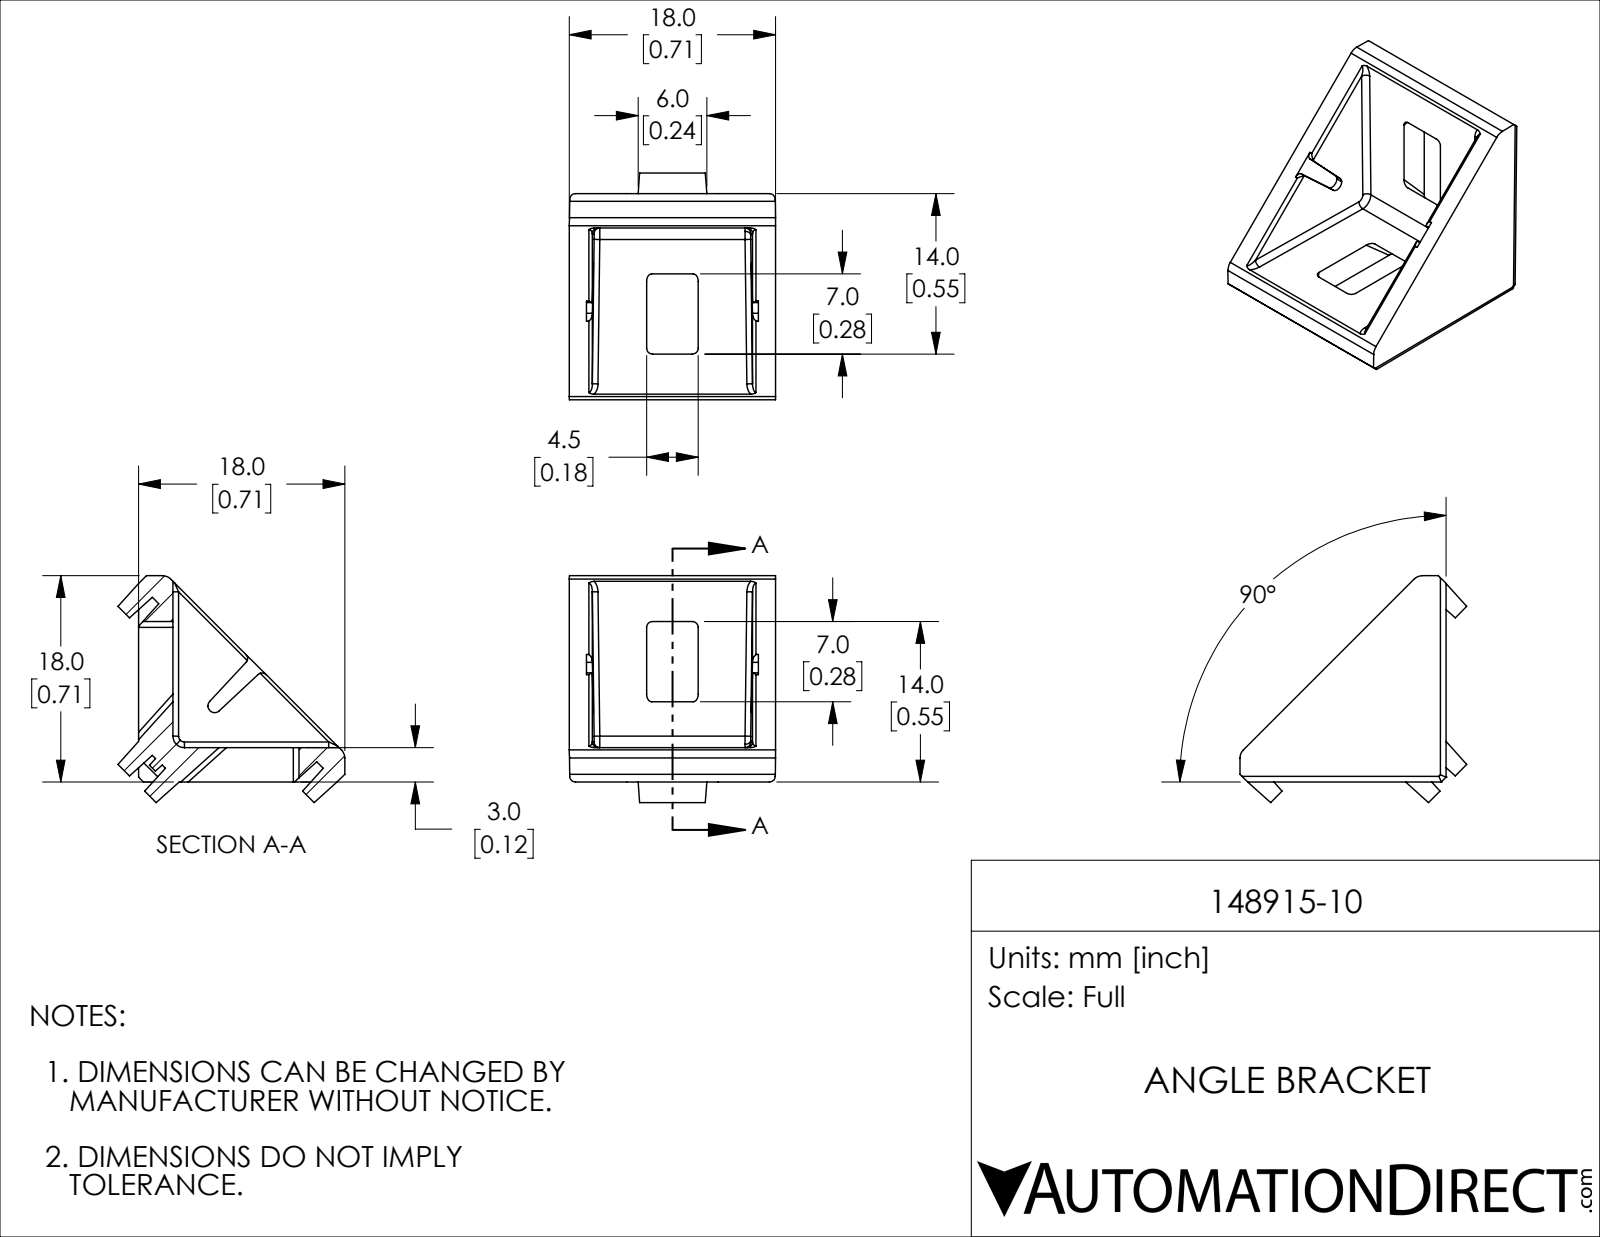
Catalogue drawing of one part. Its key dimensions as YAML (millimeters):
part_name: "148915-10"
step_written_by: "SolidWorks 2024 (CONFIG_CONTROL_DESIGN)"
units: millimeters
bodies: {solids: 1, faces: 176, planar: 88, cylindrical: 65, other: 23}
overall_size: [19.8, 19.8, 18]
volume: 1747
surface_area: 2075
partial_cylinders:
  - {radius: 0.3, count: 30}
  - {radius: 0.5, count: 20}
  - {radius: 1, count: 3}
  - {radius: 0.59, count: 1}
face_to_face_distances: [3, 2, 1.5, 15, 18, 16.5, 4, 6.63, 20.26, 13.63]
